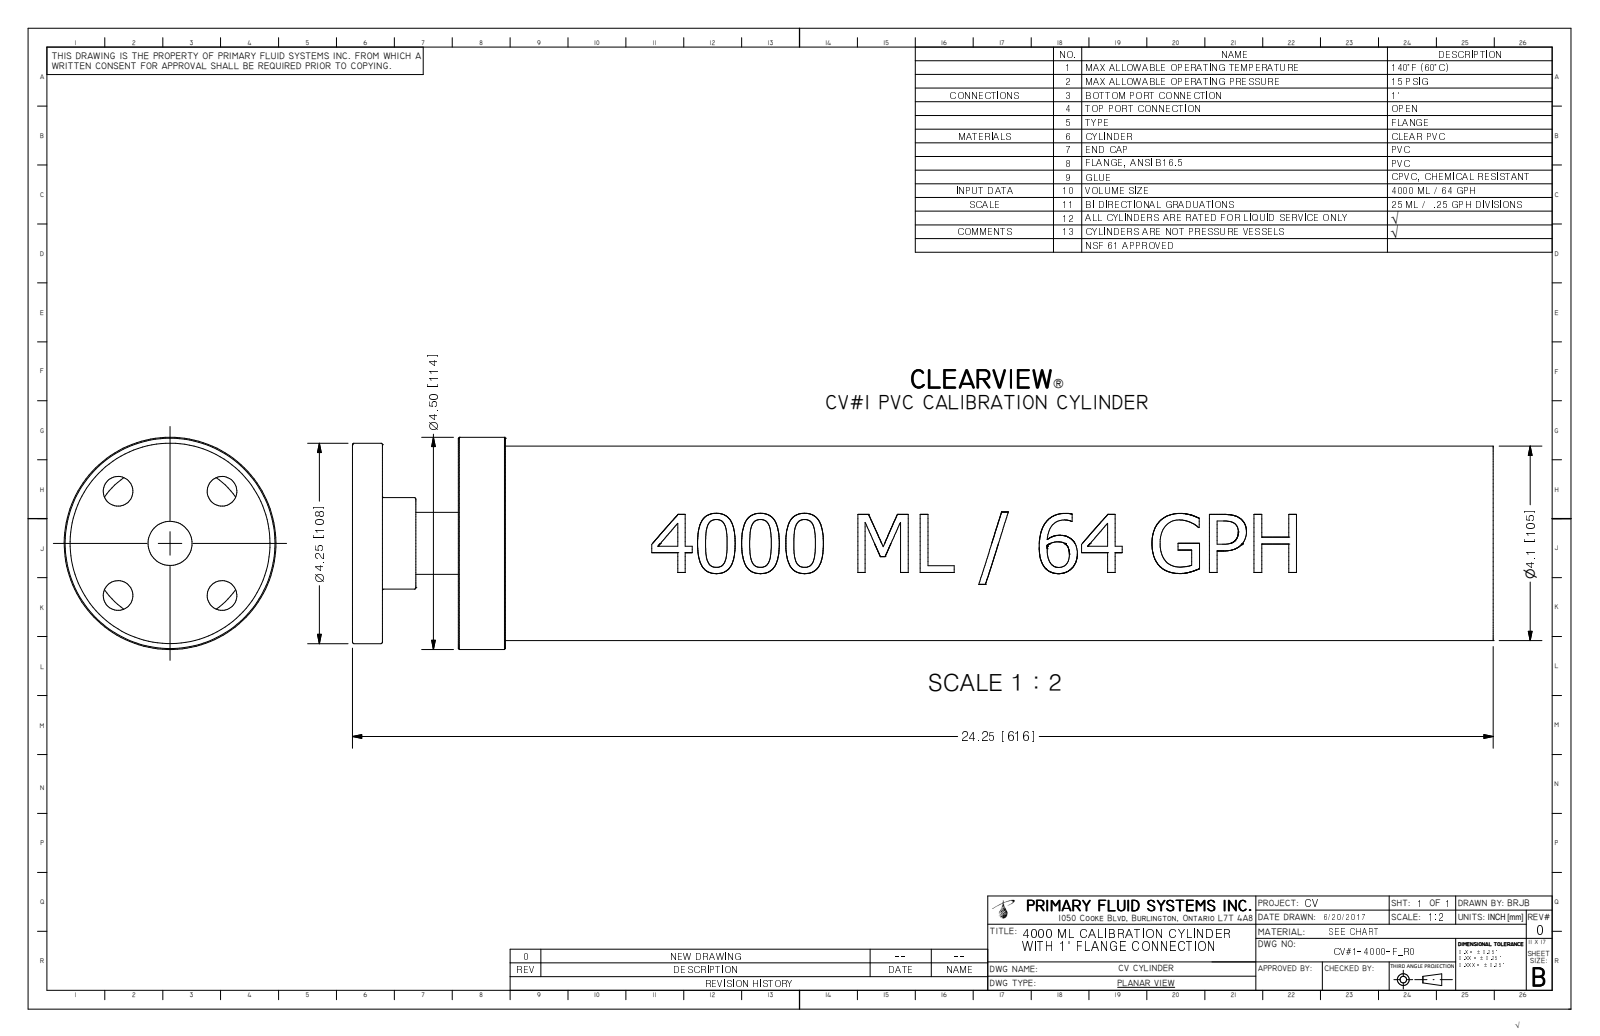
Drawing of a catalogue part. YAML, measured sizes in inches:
part_name: "PV#1-4000-F_R0"
step_written_by: "Autodesk Inventor 2009 (AUTOMOTIVE_DESIGN)"
units: inches
bodies: {solids: 1, faces: 268, planar: 95, cylindrical: 34, other: 139}
overall_size: [24.25, 4.5, 4.5]
volume: 37.33
surface_area: 680
round_holes:
  - {diameter: 0.63, count: 4}
  - {diameter: 0.936, count: 1}
  - {diameter: 0.957, count: 1}
  - {diameter: 1.156, count: 1}
  - {diameter: 4.005, count: 1}
  - {diameter: 4.15, count: 1}
round_bosses_or_shafts:
  - {diameter: 4.5, count: 1}
  - {diameter: 4.25, count: 1}
  - {diameter: 4.125, count: 1}
  - {diameter: 3.876, count: 1}
  - {diameter: 1.941, count: 1}
  - {diameter: 1.315, count: 1}
partial_cylinders:
  - {radius: 2.061, count: 1}
face_to_face_distances: [0.635, 2.25, 1.615, 0.5, 2.75, 2.115, 3.25, 2.615, 1, 1.345]
hole_center_spacings: [1.562, 2.209, 3.125]
